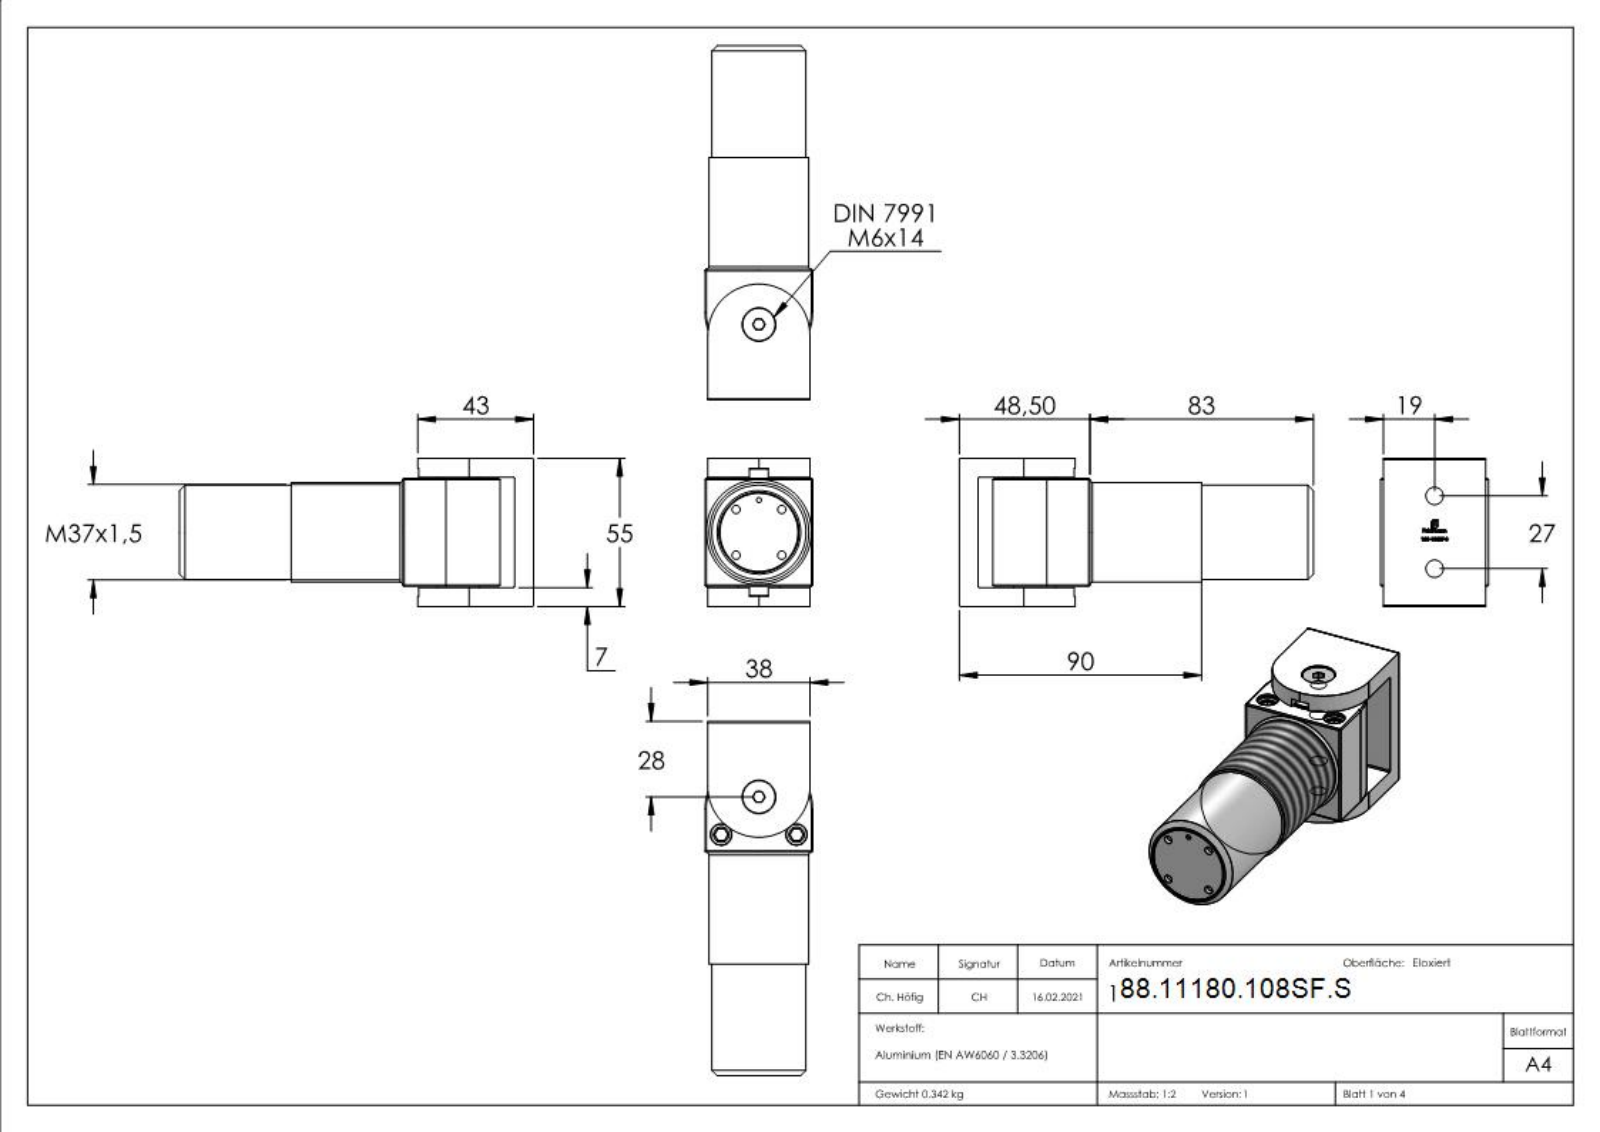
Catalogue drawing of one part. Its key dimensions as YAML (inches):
part_name: "DIN-7991 M3-M10; DIN-7991 M3-M10_DIN7991 M6x14; 180-108SF-S; Teil2_180-108SF-S Teil2 (+3 more)"
step_written_by: "SolidWorks 2018 (CONFIG_CONTROL_DESIGN)"
units: inches
bodies: {solids: 6, faces: 569, planar: 247, cylindrical: 96, other: 226}
overall_size: [551.199, 236.22, 236.22]
volume: 10.05
surface_area: 49.27
round_holes:
  - {diameter: 0.122, count: 4}
  - {diameter: 0.256, count: 3}
  - {diameter: 0.492, count: 3}
  - {diameter: 0.315, count: 2}
  - {diameter: 0.075, count: 1}
  - {diameter: 0.197, count: 1}
  - {diameter: 0.618, count: 1}
  - {diameter: 0.945, count: 1}
  - {diameter: 1.169, count: 1}
round_bosses_or_shafts:
  - {diameter: 0.307, count: 2}
  - {diameter: 1.457, count: 1}
  - {diameter: 1.378, count: 1}
  - {diameter: 1.161, count: 1}
  - {diameter: 1.024, count: 1}
  - {diameter: 0.929, count: 1}
  - {diameter: 0.61, count: 1}
  - {diameter: 0.472, count: 1}
partial_cylinders:
  - {radius: 0.02, count: 12}
  - {radius: 0.748, count: 1}
  - {radius: 0.787, count: 1}
face_to_face_distances: [0.276, 1.89, 1.87, 0.02, 0.295, 1.594, 2.165, 1.575, 0.039, 1.535]
hole_center_spacings: [0.388, 0.473, 0.669, 0.928, 0.362, 0.531, 0.78, 0.873]
